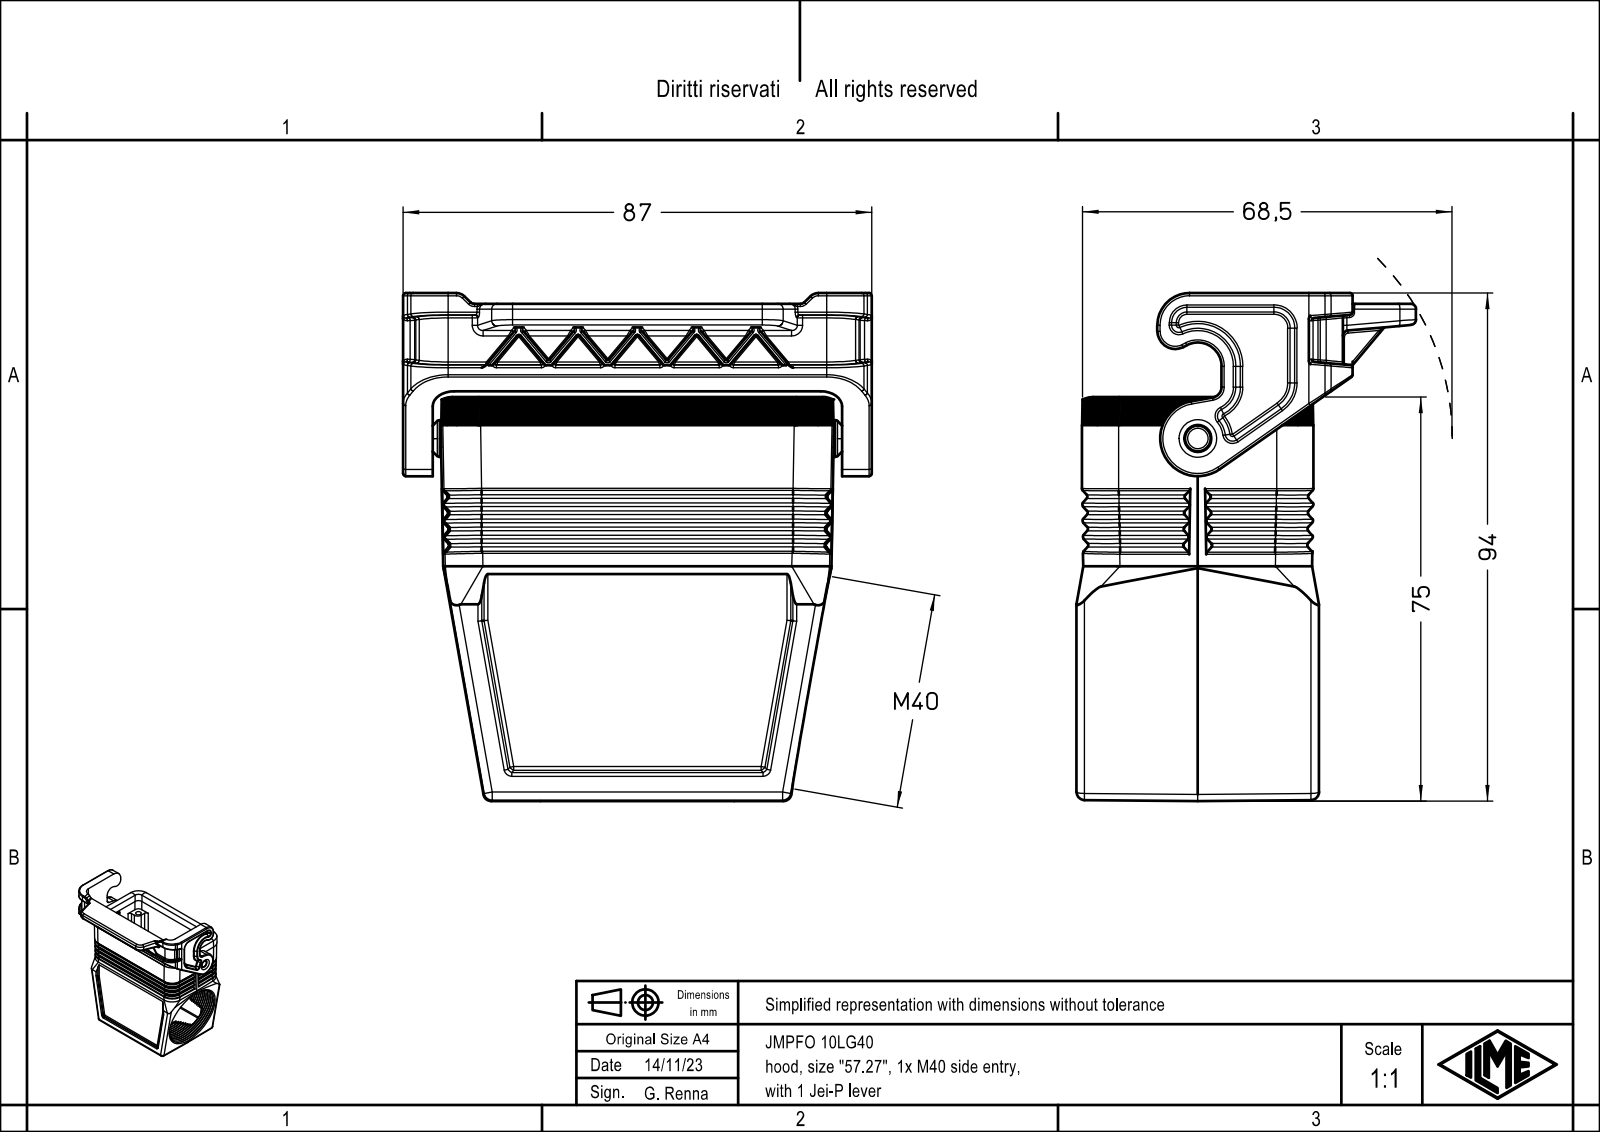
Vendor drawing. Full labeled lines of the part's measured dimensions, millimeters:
Part name (STEP PRODUCT): JMPFO 10LG40
STEP written by: Creo Elements/Direct Modeling 20.1B 02-Apr-2019 (C) Parametric Technology GmbH (AUTOMOTIVE_DESIGN)
Units: millimetres
Bodies: 1 solid, 1003 faces (273 planar, 356 cylindrical, 374 other)
Overall size (bounding box): 94.25 × 87 × 63
Volume: 82 595 mm³ · Surface area: 43 446 mm²
Round holes (diameter × count): ⌀3 ×4, ⌀3.5 ×4, ⌀4.8 ×1, ⌀38.6 ×1
Round bosses / shafts (diameter × count): ⌀6.8 ×1
Partial cylindrical surfaces — rounded edges, fillets, slot ends (radius × count): R0.5 ×96, R0.3 ×71, R1 ×35, R1.5 ×24, R0.33 ×15, R7 ×13, R3 ×12, R4 ×8
Main face-to-face distances: 39.25, 3.75, 43, 1, 4.75, 7, 35.5, 2, 34.5, 38.25
Hole centre spacings: 27, 57, 63.07
